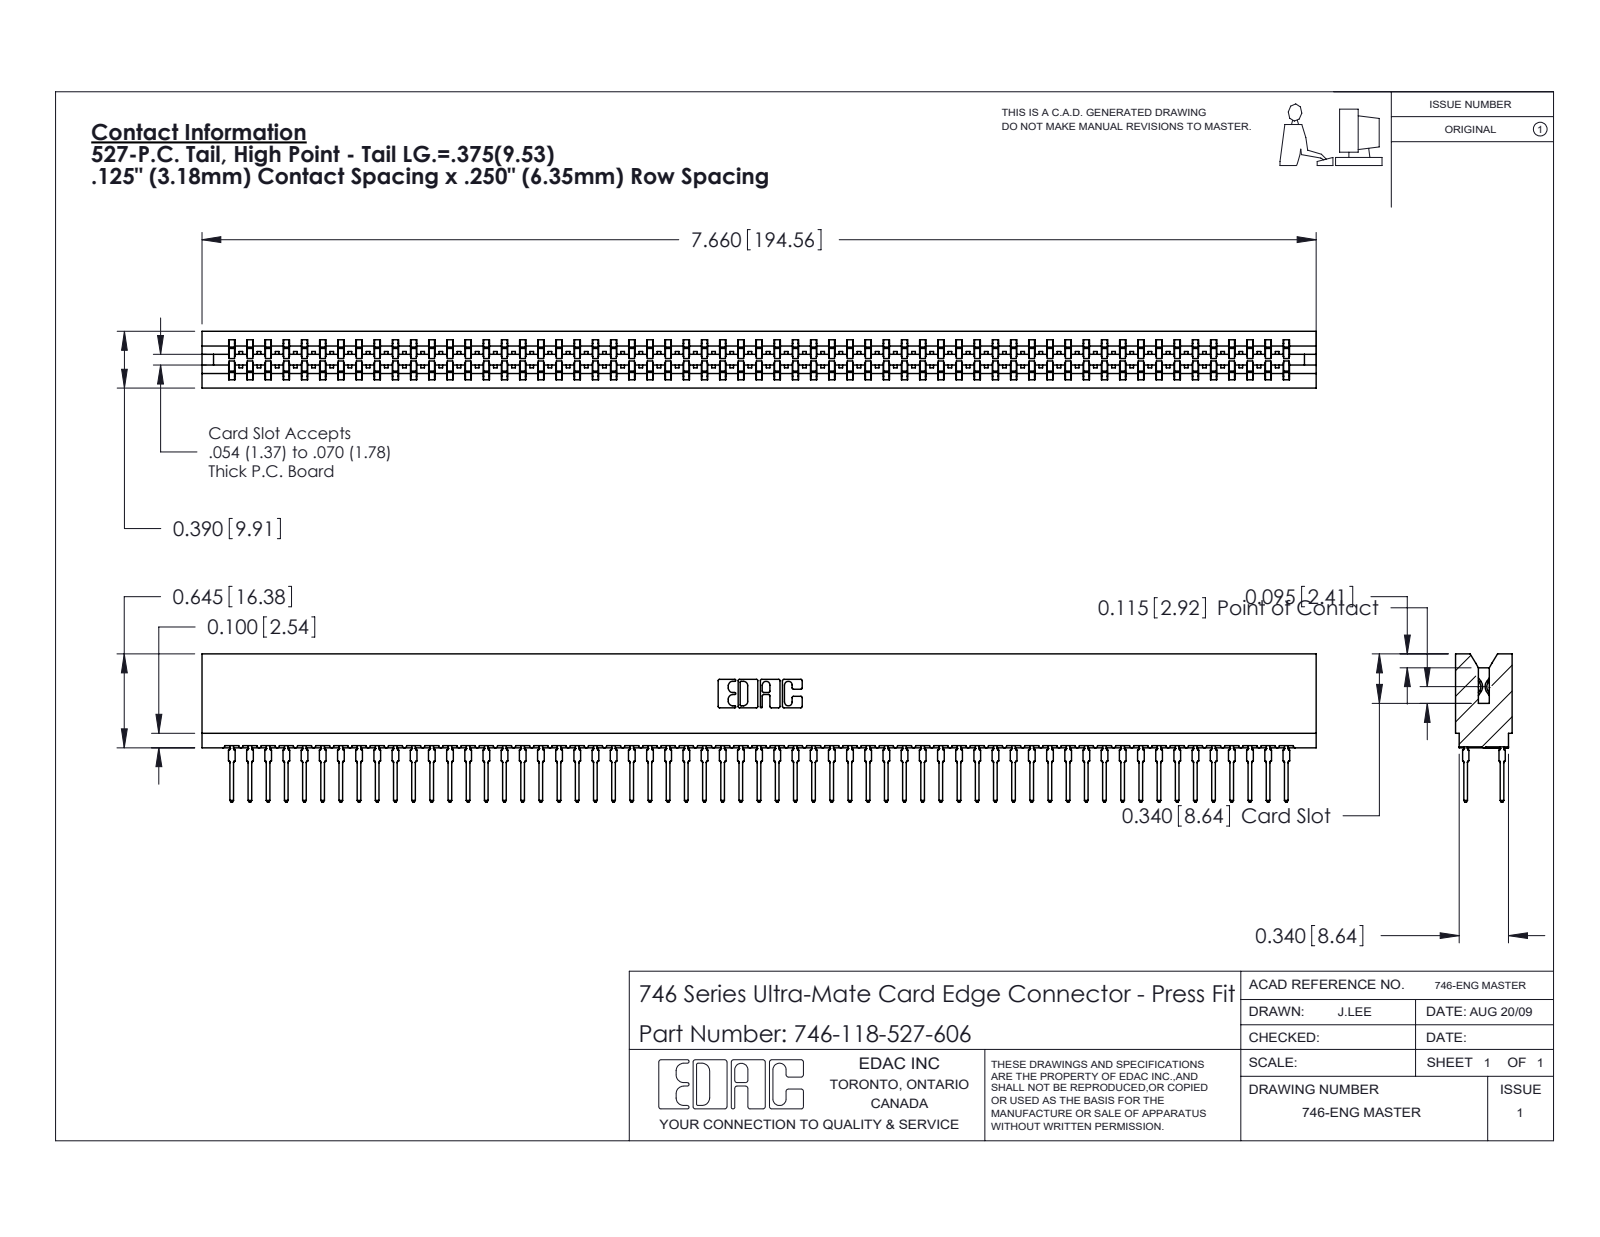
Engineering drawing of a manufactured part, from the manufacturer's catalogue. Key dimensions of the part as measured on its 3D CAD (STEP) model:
Part name (STEP PRODUCT): 746-118-527-606; 746 Part_.340 Slot Depth - 06; 746-292-001_527
STEP written by: SolidWorks 2020 (CONFIG_CONTROL_DESIGN)
Units: inches
Bodies: 119 solids, 10659 faces (5484 planar, 2107 cylindrical, 3068 other)
Overall size (bounding box): 7.66 × 1.019 × 0.39
Volume: 1.37 in³ · Surface area: 52.98 in²
Partial cylindrical surfaces — rounded edges, fillets, slot ends (radius × count): R0.021 ×236, R0.015 ×60, R0.01 ×22, R0.005 ×8, R0.011 ×8, R0.007 ×6, R0.031 ×6, R0.026 ×3
Main face-to-face distances: 0.057, 0.333, 0.39, 0.025, 0.307, 0.25, 0.275, 0.083, 0.015, 0.059
